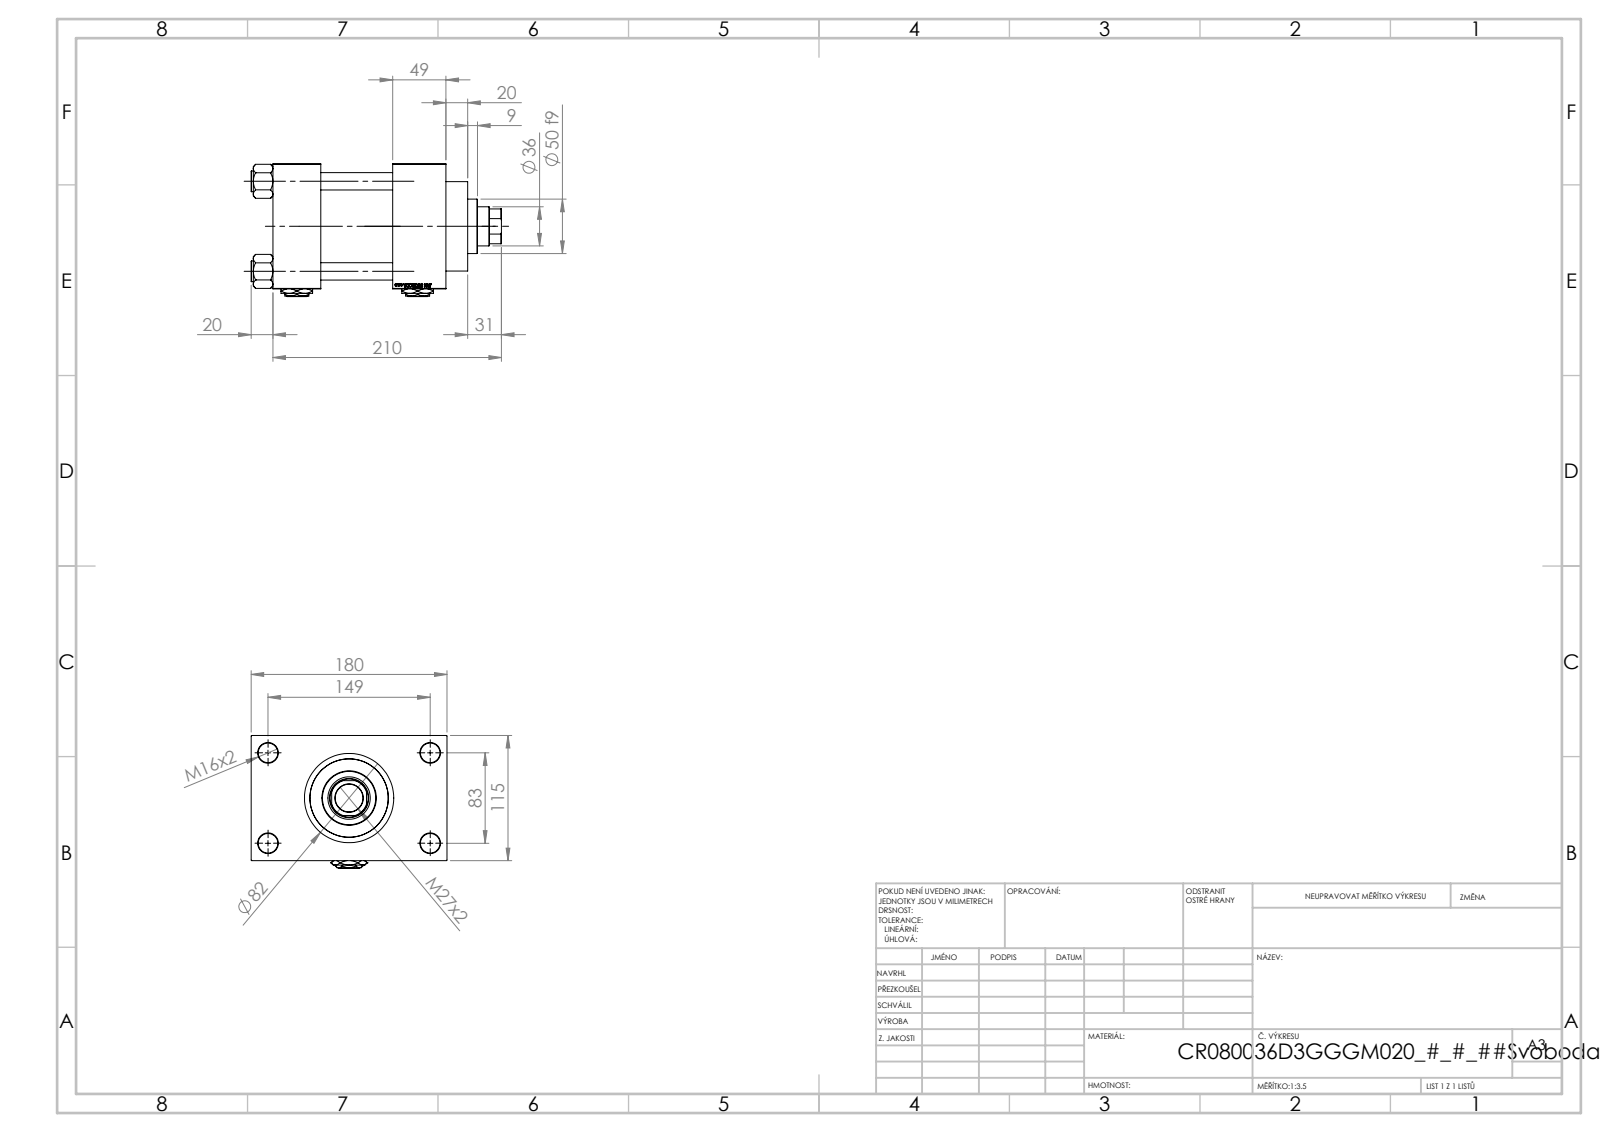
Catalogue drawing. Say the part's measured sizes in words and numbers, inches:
The part is named "V215CR_VCP_D; V215CR_D_TYCINKA; V215_VC_A; NUT_M5_D (+2 more)". Its 3-D file was written by "SolidWorks 2019 (CONFIG_CONTROL_DESIGN)". It is 13 solids with 1253 faces: 593 planar, 100 cylindrical and 560 other. Overall it measures 9.055 by 7.087 by 4.803 inches. Its volume is 121 cubic inches and its surface area 466 square inches. Round holes: 4 of diameter 0.63, 4 of diameter 0.709, 2 of diameter 0.276, 2 of diameter 1.041, 2 of diameter 1.378, 1 of diameter 1.004, 1 of diameter 1.417, 1 of diameter 1.535, 1 of diameter 2.402, 1 of diameter 2.835, 1 of diameter 3.15. Round bosses or shafts: 4 of diameter 0.748, 1 of diameter 3.386, 1 of diameter 3.228, 1 of diameter 1.969. Partial cylindrical surfaces (rounded edges, fillets, slot ends): 1 of radius 0.689. The main face-to-face distances are 4.528, 2.598, 4.331, 1.929, 1.732, 6.26, 5.807, 1.28, 0.787, 2.717. The hole center spacings are 1.305, 2.302, 3.256, 3.357, 3.513, 4.561, 5.607, 3.268.
